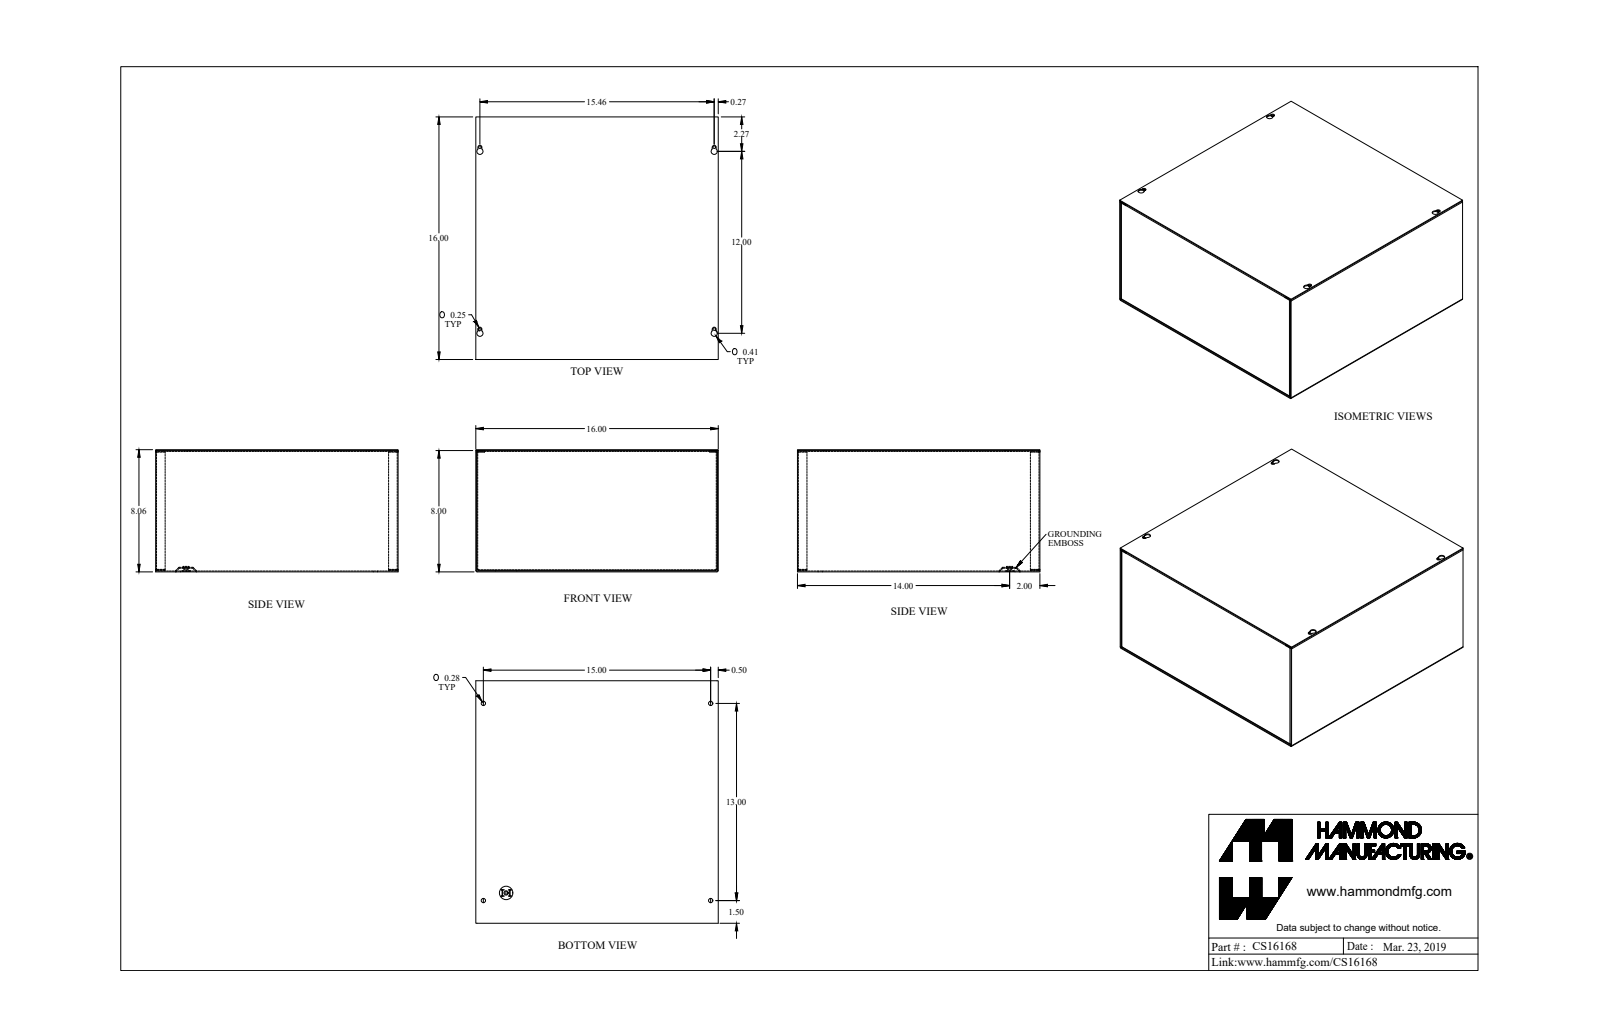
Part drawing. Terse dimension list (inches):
name: CS16168_Default
written by: SolidWorks 2019 (CONFIG_CONTROL_DESIGN)
unit: in
bodies: 4 solids, 205 faces (125 planar, 72 cylindrical, 8 other)
size: 16 × 16 × 8.057
volume: 61.3 in³; area: 2 167 in²
holes: 5× ⌀0.17, 4× ⌀0.281, 1× ⌀0.5
bosses: 1× ⌀0.492, 1× ⌀0.284
rounds: 12× R0.029, 12× R0.086, 8× R0.057, 4× R0.125, 4× R0.203
face distances: 0.057, 8, 15.943, 7.943, 8.057, 16, 15.886, 0.08, 7.863, 7.92
hole spacings: 0.55, 12.502, 15.238, 19.703, 12, 13, 15, 15.46
